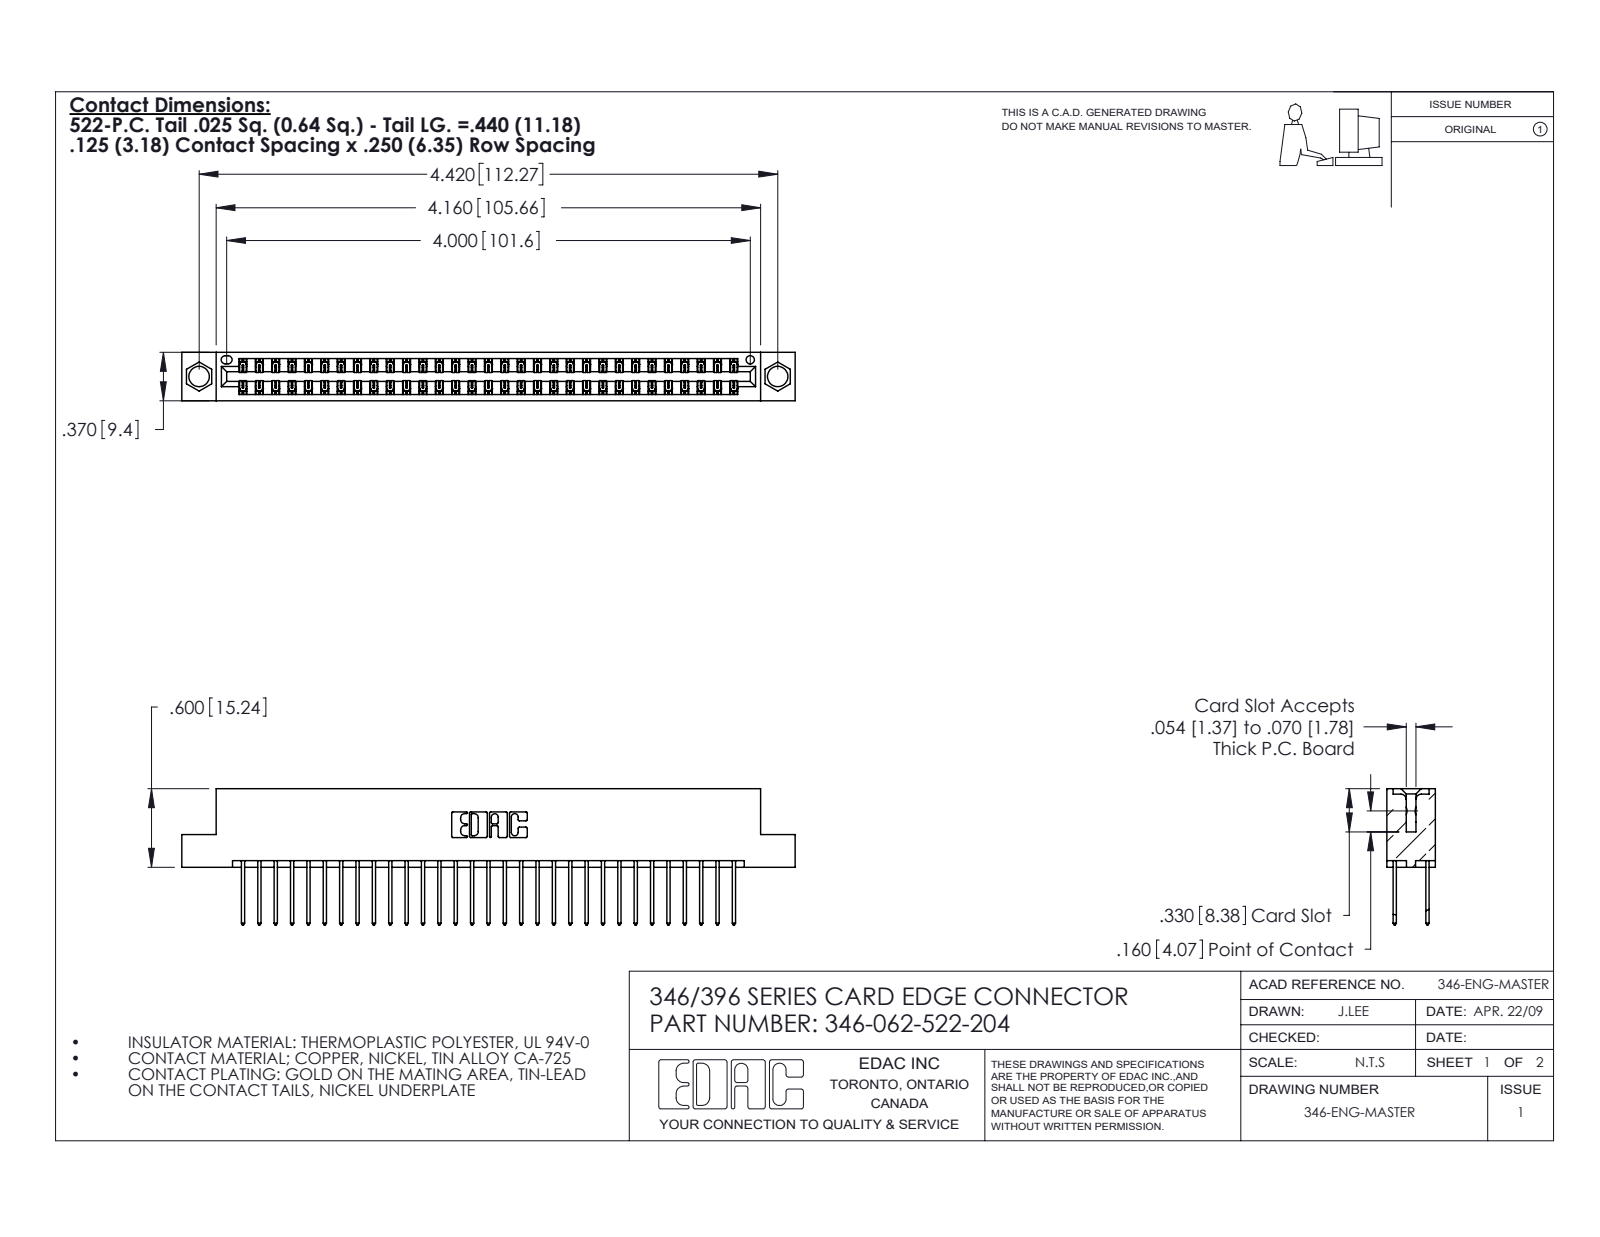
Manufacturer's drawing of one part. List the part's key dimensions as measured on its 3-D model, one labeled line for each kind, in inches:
Part name (STEP PRODUCT): 345-292-001_345-293-122; 346 Part_Flush Mounting Lugs - 0.156 Dia-TH; 346-062-522-204
STEP written by: SolidWorks 2020 (CONFIG_CONTROL_DESIGN)
Units: inches
Bodies: 63 solids, 3360 faces (2260 planar, 1100 cylindrical, 0 other)
Overall size (bounding box): 4.685 × 1.04 × 0.37
Volume: 0.706 in³ · Surface area: 25.29 in²
Round holes (diameter × count): ⌀0.156 ×2, ⌀0.064 ×1
Partial cylindrical surfaces — rounded edges, fillets, slot ends (radius × count): R0.006 ×93, R0.01 ×62, R0.01 ×22, R0.007 ×6, R0.031 ×6, R0.026 ×3, R0.014 ×2, R0.022 ×2
Main face-to-face distances: 0.048, 0.322, 0.25, 0.37, 0.072, 0.298, 0.025, 0.275, 0.148, 0.222
Hole centre spacings: 0.246, 4.212, 4.42
